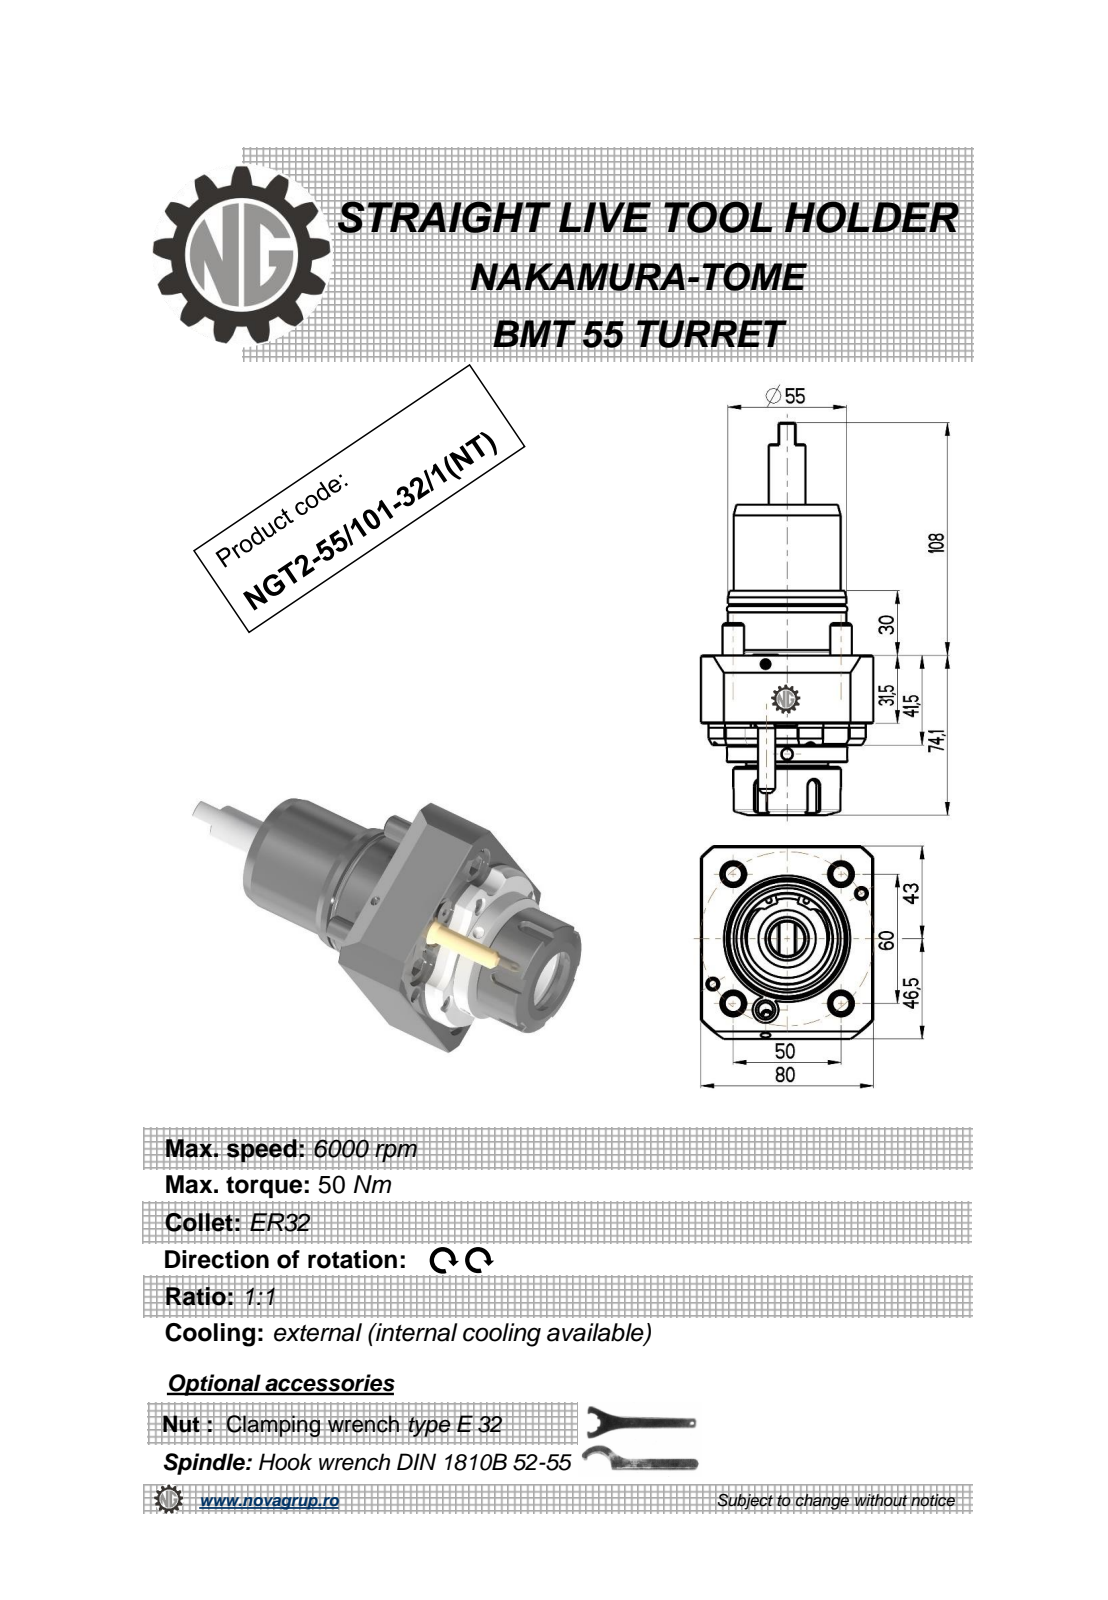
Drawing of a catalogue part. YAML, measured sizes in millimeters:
part_name: "NGT2_55_101_32_1_NT"
step_written_by: "PRO/ENGINEER BY PARAMETRIC TECHNOLOGY CORPORATION, 2010280 (CONFIG_CONTROL_DESIGN)"
units: millimeters
bodies: {solids: 2, faces: 272, planar: 91, cylindrical: 77, other: 104}
overall_size: [182.1, 91.1, 80]
volume: 480173
surface_area: 54348
round_holes:
  - {diameter: 5, count: 3}
  - {diameter: 3, count: 1}
  - {diameter: 6.8, count: 1}
  - {diameter: 27, count: 1}
round_bosses_or_shafts:
  - {diameter: 10, count: 4}
  - {diameter: 56, count: 1}
  - {diameter: 55, count: 1}
  - {diameter: 54.4, count: 1}
  - {diameter: 50, count: 1}
  - {diameter: 49.7, count: 1}
  - {diameter: 42, count: 1}
  - {diameter: 17, count: 1}
partial_cylinders:
  - {radius: 0.22, count: 6}
  - {radius: 3, count: 5}
  - {radius: 8.5, count: 4}
  - {radius: 0.8, count: 2}
  - {radius: 6, count: 2}
  - {radius: 20.44, count: 1}
  - {radius: 30.55, count: 1}
  - {radius: 36.5, count: 1}
face_to_face_distances: [31.5, 80, 10, 41.5, 18, 70, 101.5, 111.5, 89.5, 20.1]
hole_center_spacings: [2.55, 34.48, 36.75]
